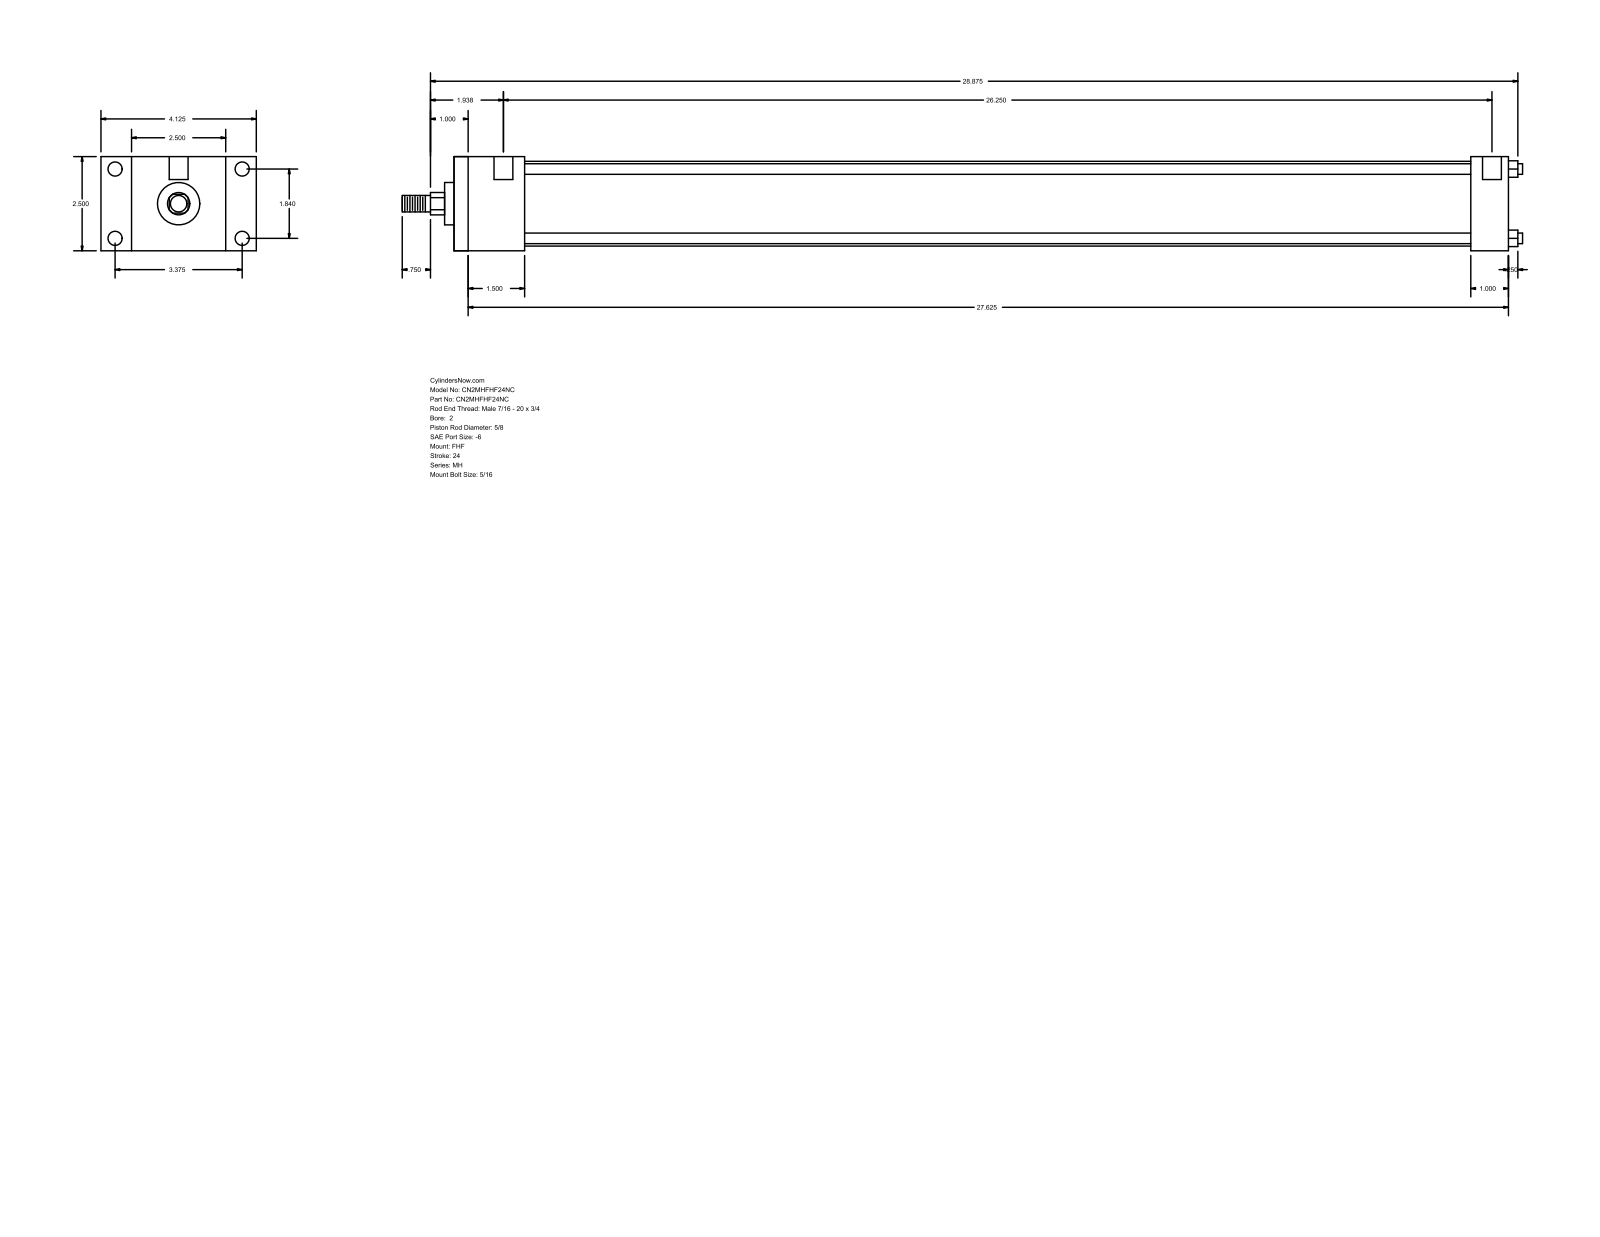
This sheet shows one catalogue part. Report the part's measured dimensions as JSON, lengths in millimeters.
{"part_name": "MH_FHF__0200_0.625", "step_written_by": "GSSL Pune (CONFIG_CONTROL_DESIGN)", "units": "millimeters", "bodies": {"solids": 0, "faces": 88, "planar": 60, "cylindrical": 28, "other": 0}, "overall_size": [755.65, 104.78, 63.5], "round_holes": [[5.56, 4], [9.53, 4], [12.7, 2]], "round_bosses_or_shafts": [[7.14, 4], [57.15, 1], [28.57, 1], [15.88, 1], [11.11, 1]], "partial_cylinders_radius": [[7.54, 1]], "face_to_face_distances": [63.5, 47.62, 711.2, 663.58, 20.64, 84.14, 104.78, 685.79, 638.17, 25.41], "hole_center_spacings": [46.74, 85.72, 97.63, 674.69, 3.18, 4.76, 666.75, 669.93]}
